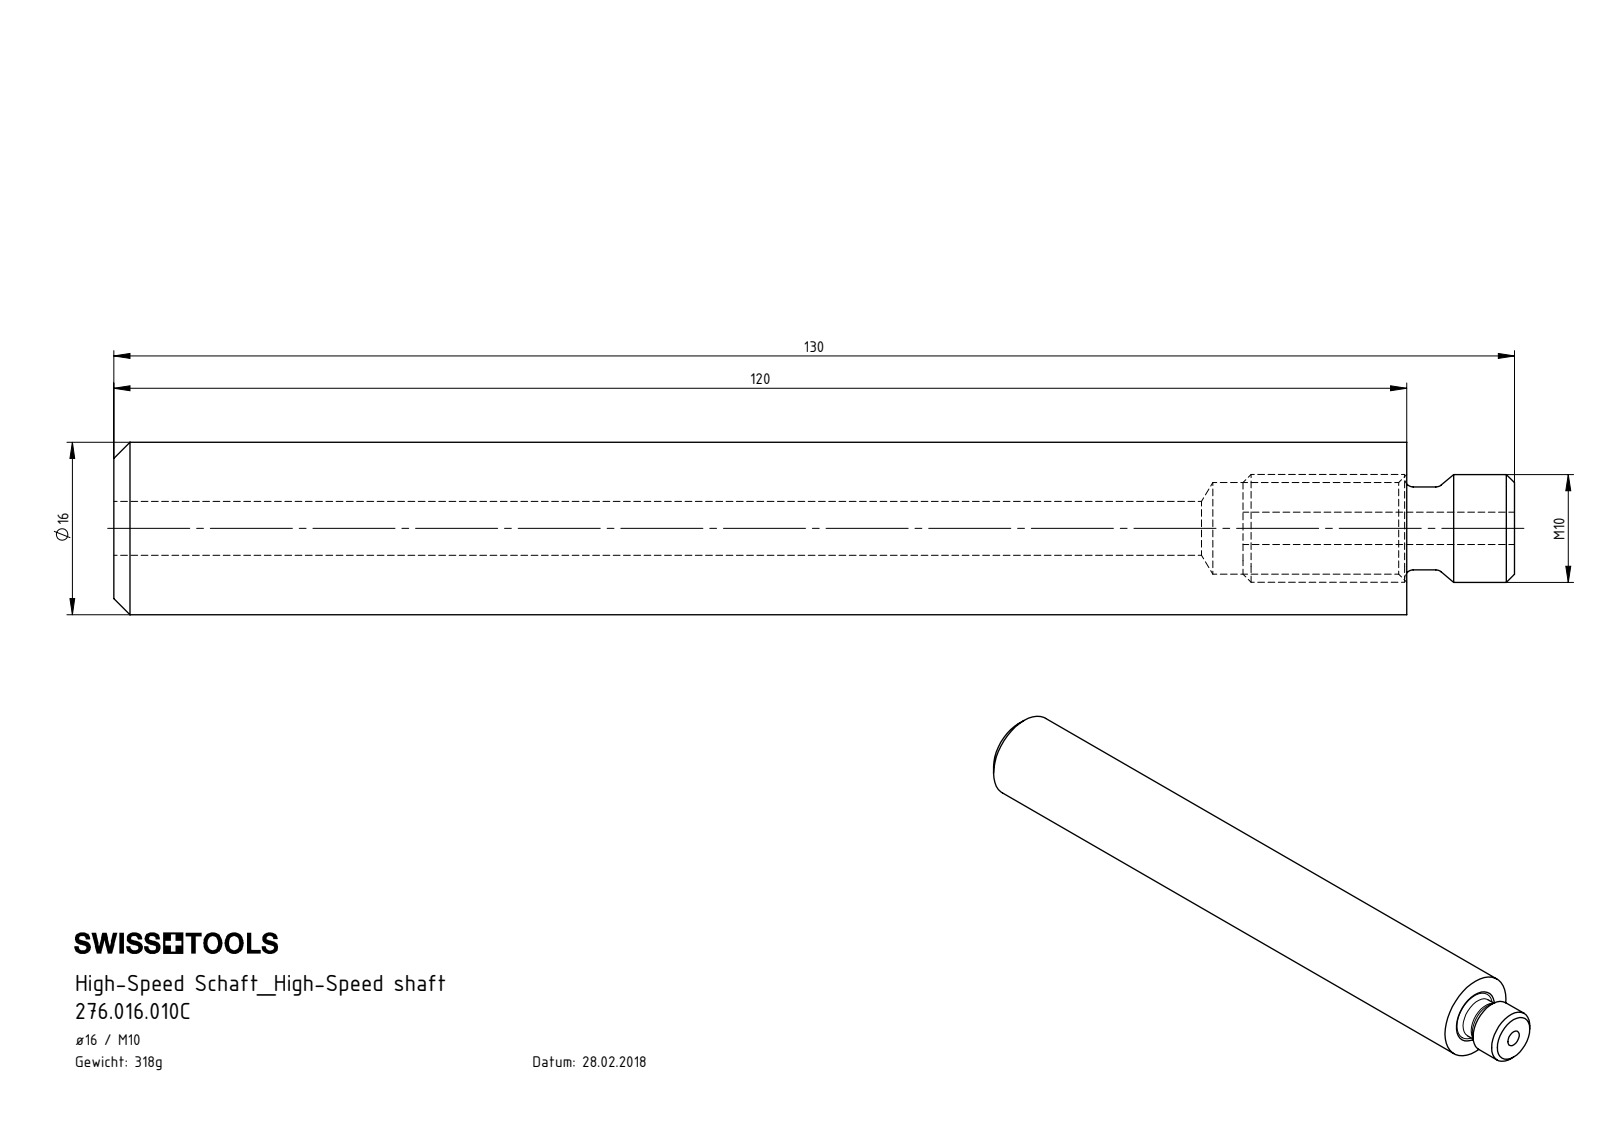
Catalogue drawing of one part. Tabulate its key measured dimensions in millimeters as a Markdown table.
| quantity | value |
| --- | --- |
| part name | 276.016.010C; HM1-BG1.010.025_A; HM1-U16.001.120_A |
| STEP written by | SolidWorks 2017 (CONFIG_CONTROL_DESIGN) |
| units | millimeters |
| bodies | 2 solids, 35 faces (5 planar, 14 cylindrical, 16 other) |
| overall size | 130 × 16 × 16 |
| volume | 22 687 mm³ |
| surface area | 9 559 mm² |
| round holes (diameter × count) | 3 × 1, 5 × 1, 8.5 × 1 |
| round bosses / shafts (diameter × count) | 16 × 1, 10 × 1, 7.7 × 1 |
| main face-to-face distances | 120, 130, 10, 104.8, 15.2, 25.2, 119.8, 15, 10.2 |
